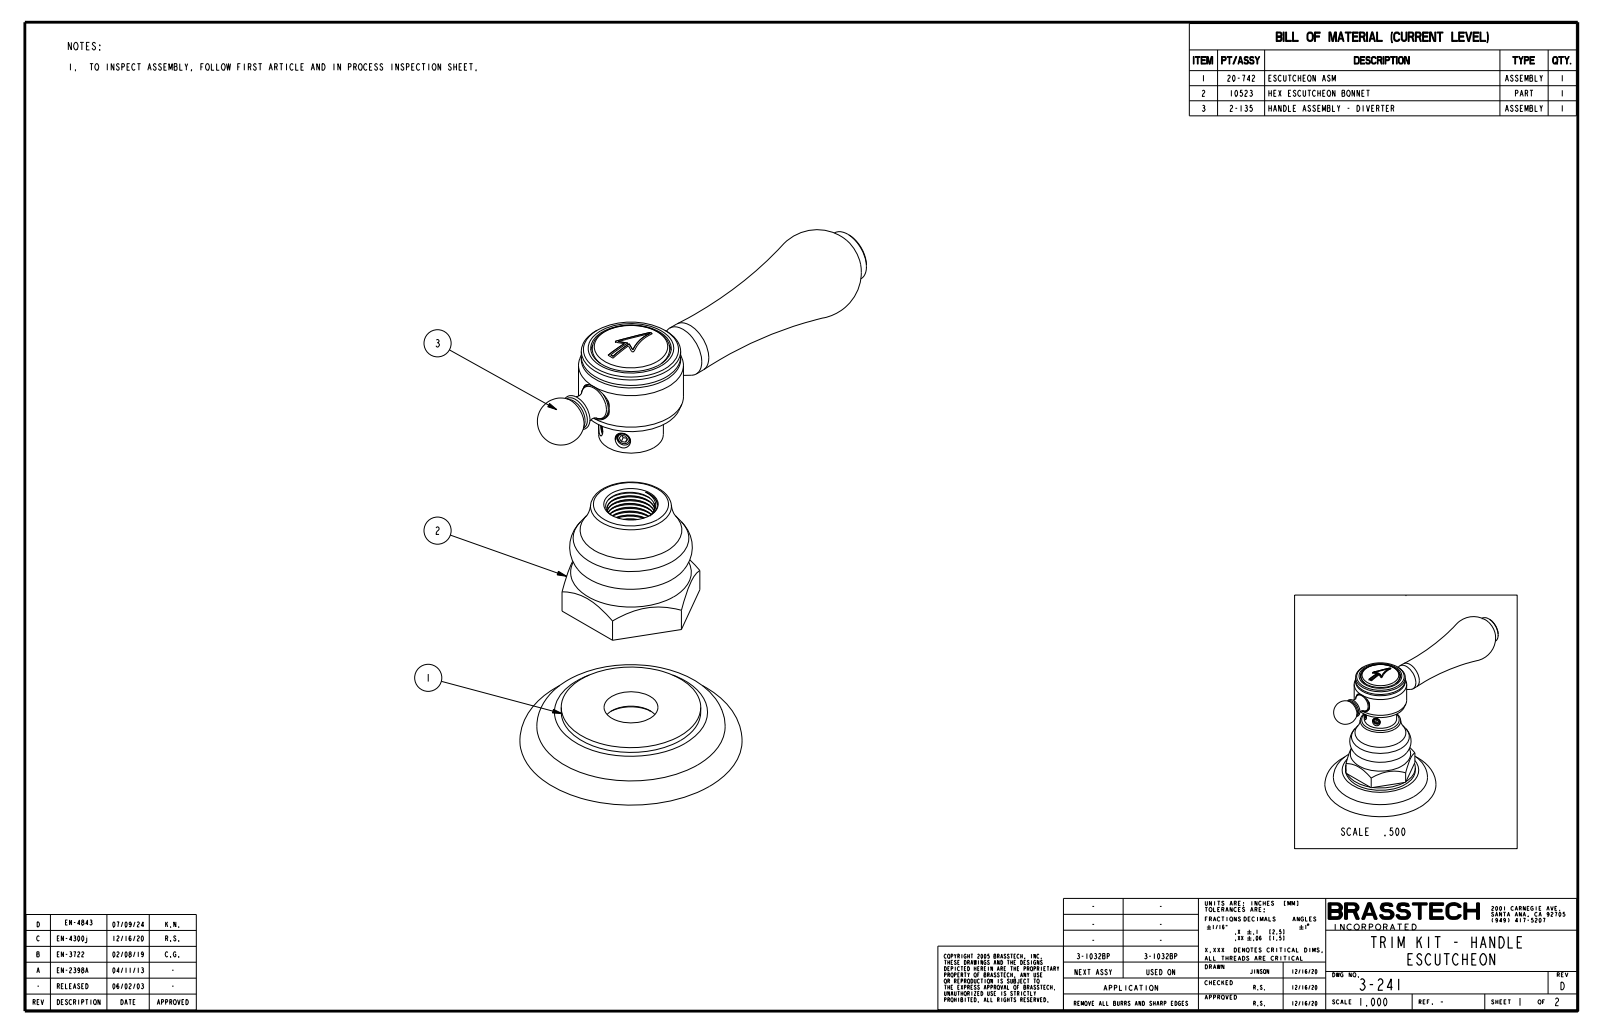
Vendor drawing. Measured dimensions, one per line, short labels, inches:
name: 3-241
written by: CREO PARAMETRIC BY PTC INC, 2018400 (CONFIG_CONTROL_DESIGN)
unit: in
bodies: 1 solid, 130 faces (43 planar, 29 cylindrical, 58 other)
size: 4.675 × 2.902 × 2.36
volume: 4.795 in³; area: 26.55 in²
holes: 1× ⌀0.41
bosses: 1× ⌀1.482, 1× ⌀1.115, 1× ⌀1.055, 1× ⌀0.687, 1× ⌀0.563, 1× ⌀0.4, 1× ⌀0.394, 1× ⌀0.392
rounds: 2× R0.015, 2× R1, 2× R1.02, 1× R0.02
face distances: 1.313, 1.687, 0.375, 1.312, 0.02, 1.707, 1.332, 1.313, 0.437, 0.062
